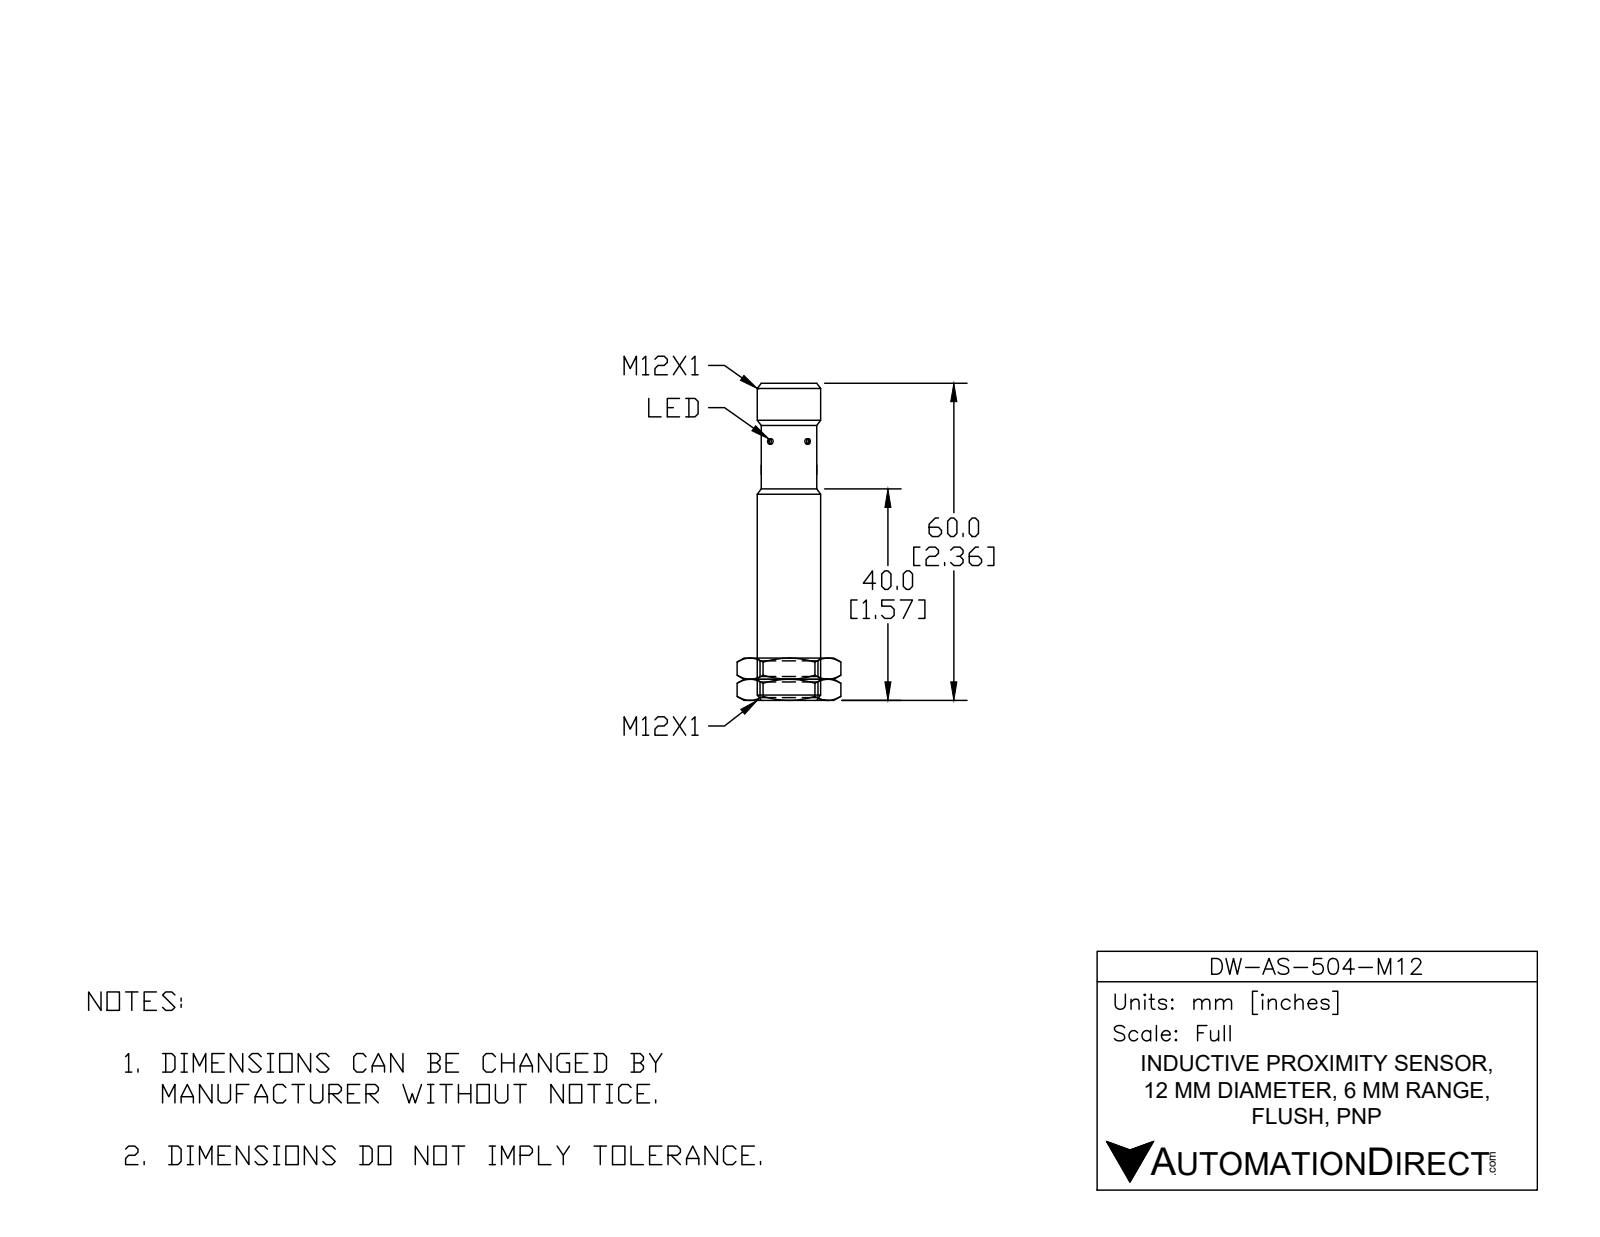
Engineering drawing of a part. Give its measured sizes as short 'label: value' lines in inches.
name: DW-AS-504-M12
written by: SolidWorks 2017 (AUTOMOTIVE_DESIGN)
unit: in
bodies: 1 solid, 35 faces (7 planar, 19 cylindrical, 9 other)
size: 2.362 × 0.472 × 0.472
volume: 0.367 in³; area: 4.348 in²
holes: 2× ⌀0.118, 1× ⌀0.335
bosses: 4× ⌀0.039, 1× ⌀0.472, 1× ⌀0.415
rounds: 2× R0.022, 1× R0.193
face distances: 2.02, 2.362, 0.343, 0.043, 1.614, 0.406, 0.748, 2.047, 0.433, 0.028
